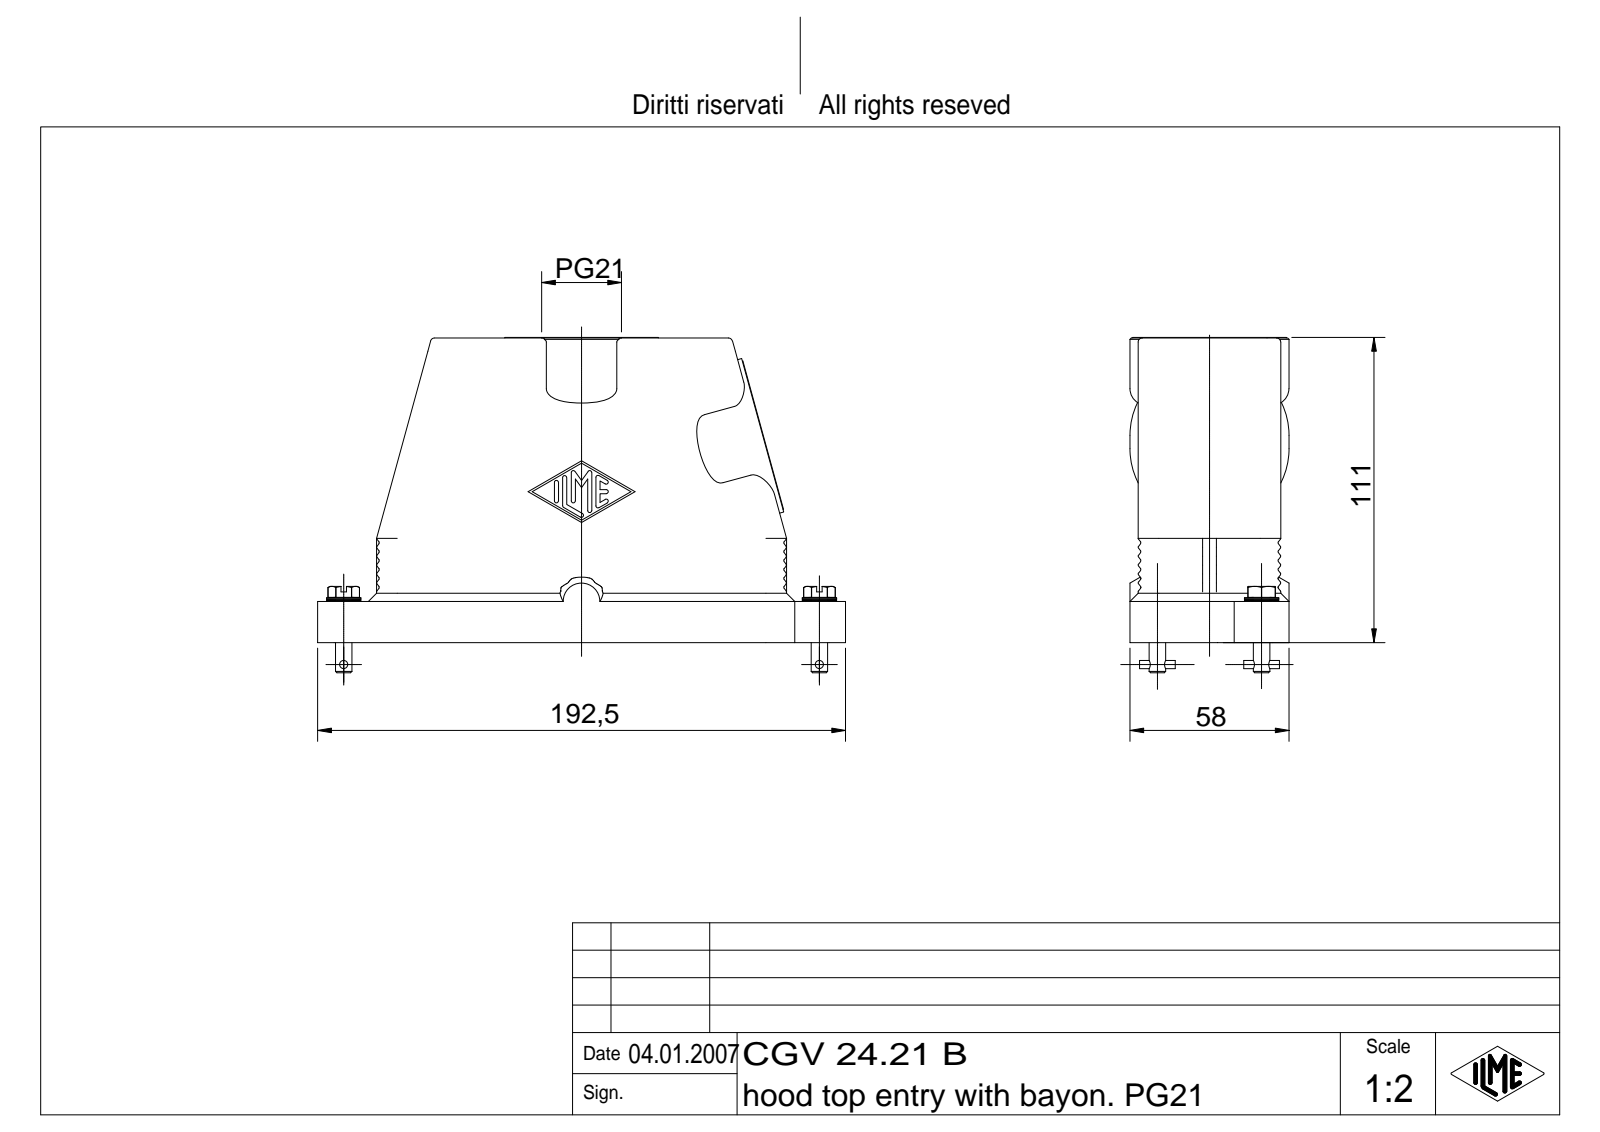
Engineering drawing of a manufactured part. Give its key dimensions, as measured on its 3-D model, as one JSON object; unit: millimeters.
{"part_name": "CGV 24.21 B", "step_written_by": "Autodesk Inventor 7 (AUTOMOTIVE_DESIGN)", "units": "millimeters", "bodies": {"solids": 3, "faces": 779, "planar": 193, "cylindrical": 203, "other": 383}, "overall_size": [192.5, 122.2, 58], "volume_mm3": 262432, "surface_area_mm2": 107711, "round_holes": [[2.46, 2], [3.2, 2], [6.6, 2], [15, 2], [26.78, 1]], "round_bosses_or_shafts": [[58, 2], [56, 2], [12.5, 2], [6, 2], [3, 2]], "partial_cylinders_radius": [[0.5, 39], [0.75, 14], [7.5, 8], [6, 6], [1.5, 4], [3, 4], [5.75, 2], [10.5, 2]], "face_to_face_distances": [3, 52, 49, 46, 6, 55, 2.5, 0.5, 58, 3.5], "hole_center_spacings": [35.18, 142.51, 107.45, 177.61]}
